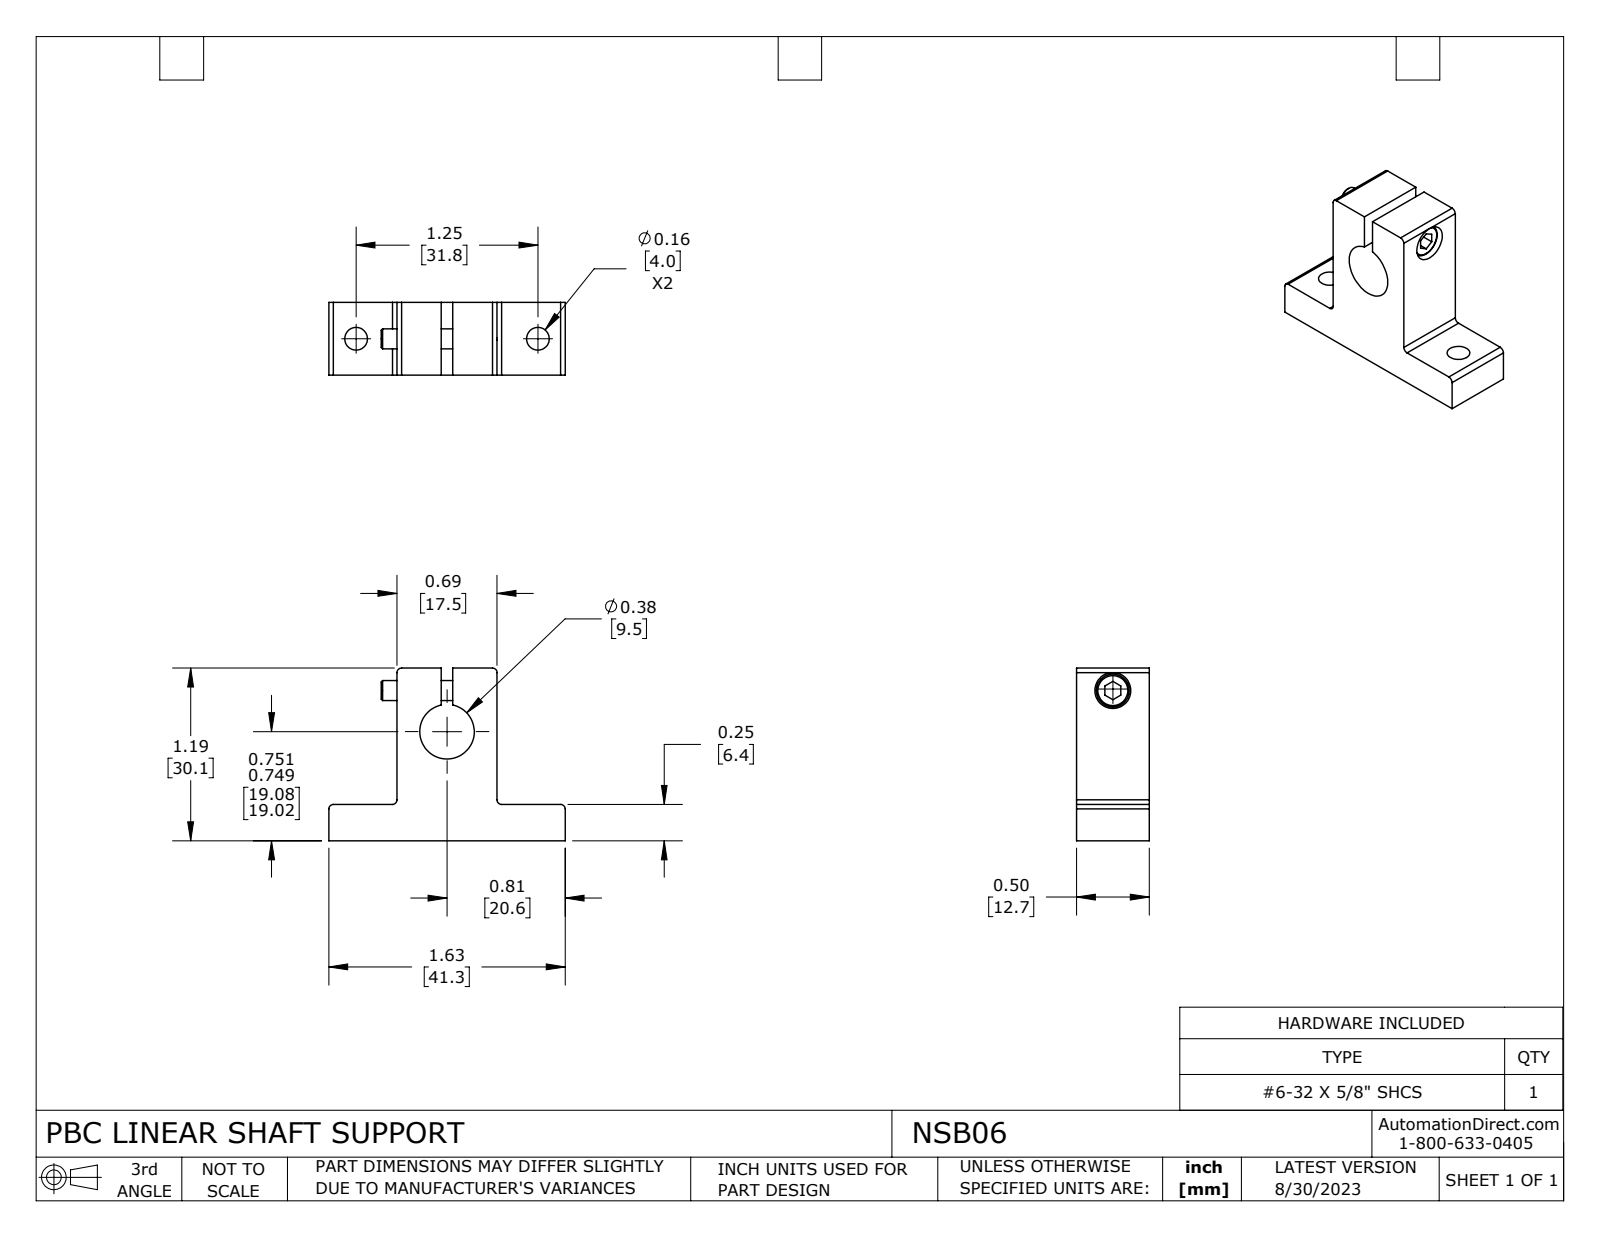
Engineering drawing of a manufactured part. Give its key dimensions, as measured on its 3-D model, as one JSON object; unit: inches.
{"part_name": "NSB06", "step_written_by": "SolidWorks 2023 (CONFIG_CONTROL_DESIGN)", "units": "inches", "bodies": {"solids": 2, "faces": 51, "planar": 24, "cylindrical": 23, "other": 4}, "overall_size": [1.625, 1.187, 0.5], "volume_in3": 0.451, "surface_area_in2": 6.265, "round_holes": [[0.156, 2], [0.107, 1], [0.164, 1], [0.247, 1], [0.375, 1]], "round_bosses_or_shafts": [[0.226, 1], [0.138, 1]], "partial_cylinders_radius": [[0.031, 6]], "face_to_face_distances": [0.5, 0.688, 0.25, 1.187, 0.937, 0.305, 0.383, 0.469, 1.157, 0.773], "hole_center_spacings": [1.25]}
